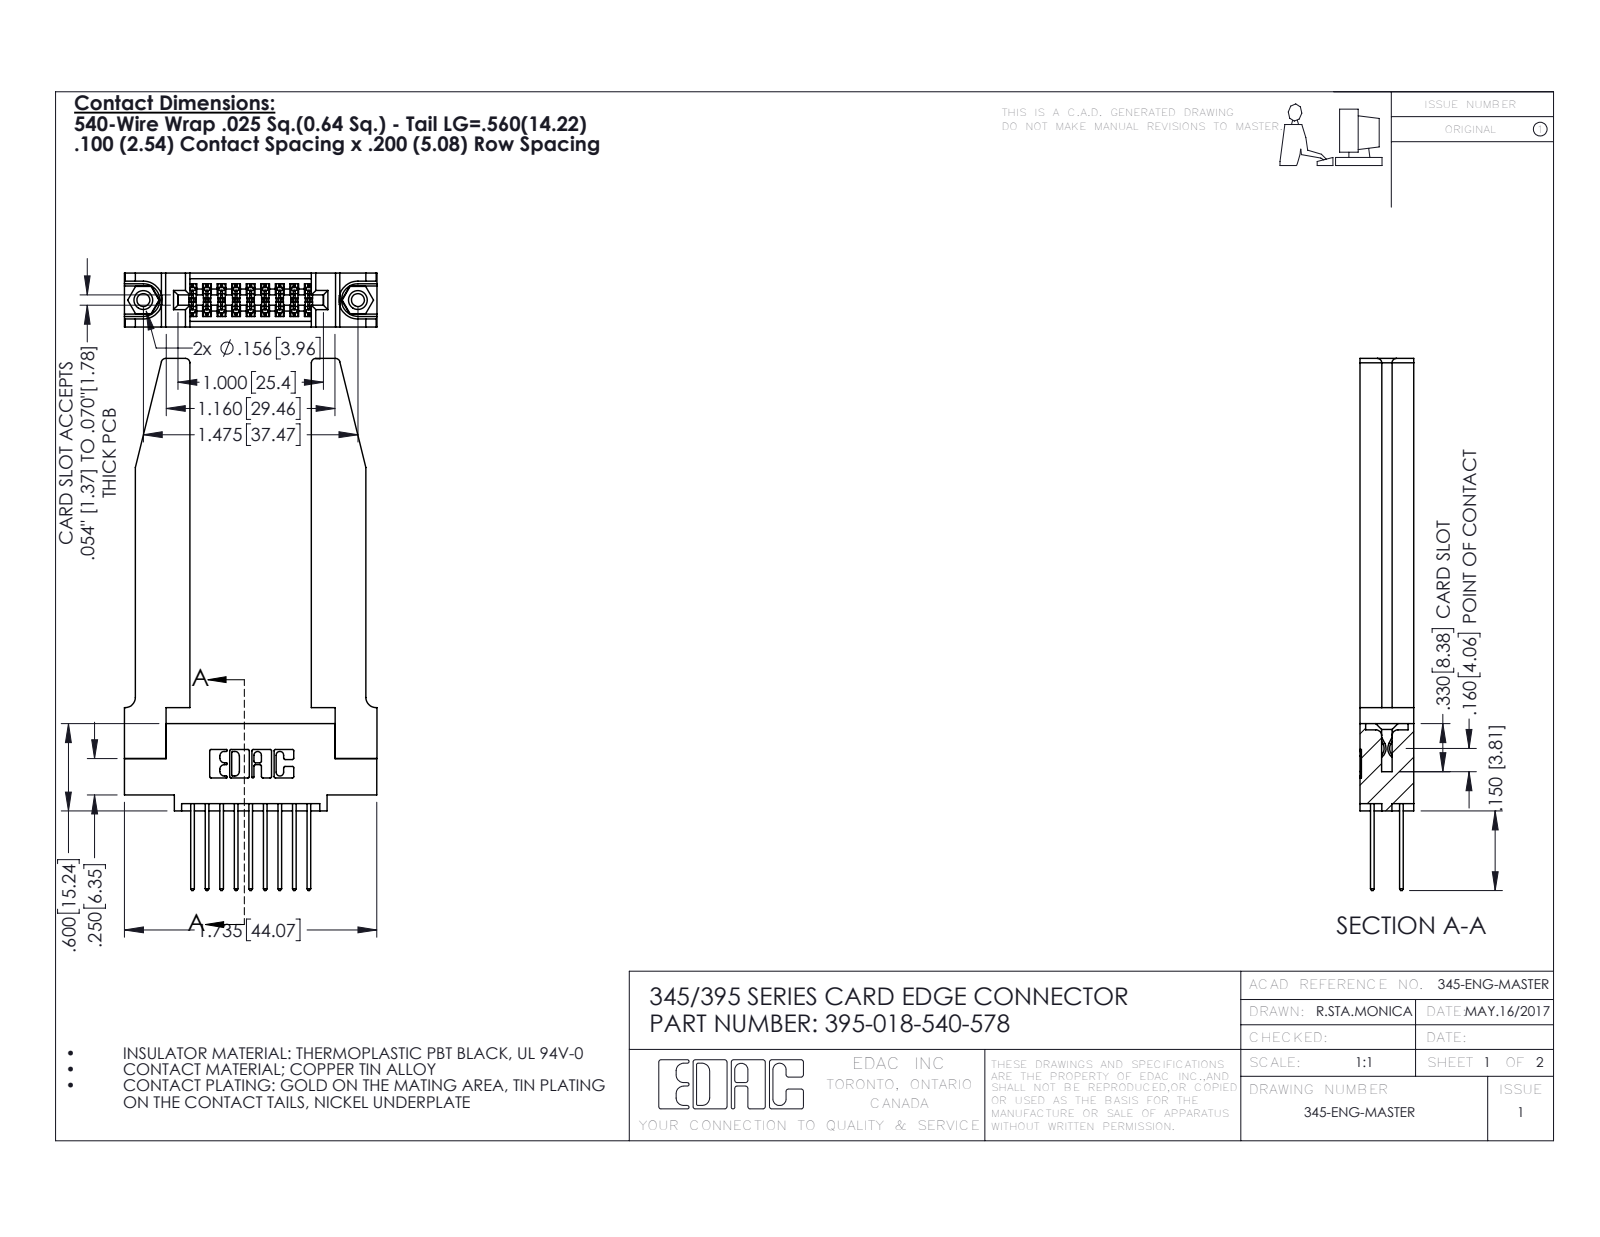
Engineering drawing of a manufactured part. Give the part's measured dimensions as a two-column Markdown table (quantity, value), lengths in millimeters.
| quantity | value |
| --- | --- |
| part name | 395-018-540-578; 345-292-001_345-293-140; 345-220-078_345-220-078; 345 Part_0.110 Offset - 0.156 Dia-TH (+1 more) |
| STEP written by | SolidWorks 2016 (CONFIG_CONTROL_DESIGN) |
| units | millimeters |
| bodies | 23 solids, 1264 faces (820 planar, 392 cylindrical, 52 other) |
| overall size | 92.9 × 44.1 × 9.4 |
| volume | 11 700 mm³ |
| surface area | 12 480 mm² |
| round holes (diameter × count) | 2.3 × 2, 3.2 × 2, 4 × 2, 1.6 × 1 |
| round bosses / shafts (diameter × count) | 3.9 × 2 |
| partial cylindrical surfaces (radius × count) | 0.2 × 27, 0.3 × 22, 0.3 × 18, 0.8 × 8, 0.2 × 6, 0.8 × 6, 0.7 × 3, 0.4 × 2 |
| main face-to-face distances | 9.4, 1.8, 7.6, 3.8, 3.8, 5.6, 2, 2.5, 6.9, 0.6 |
| hole center spacings | 6.9, 31.6, 37.5 |
